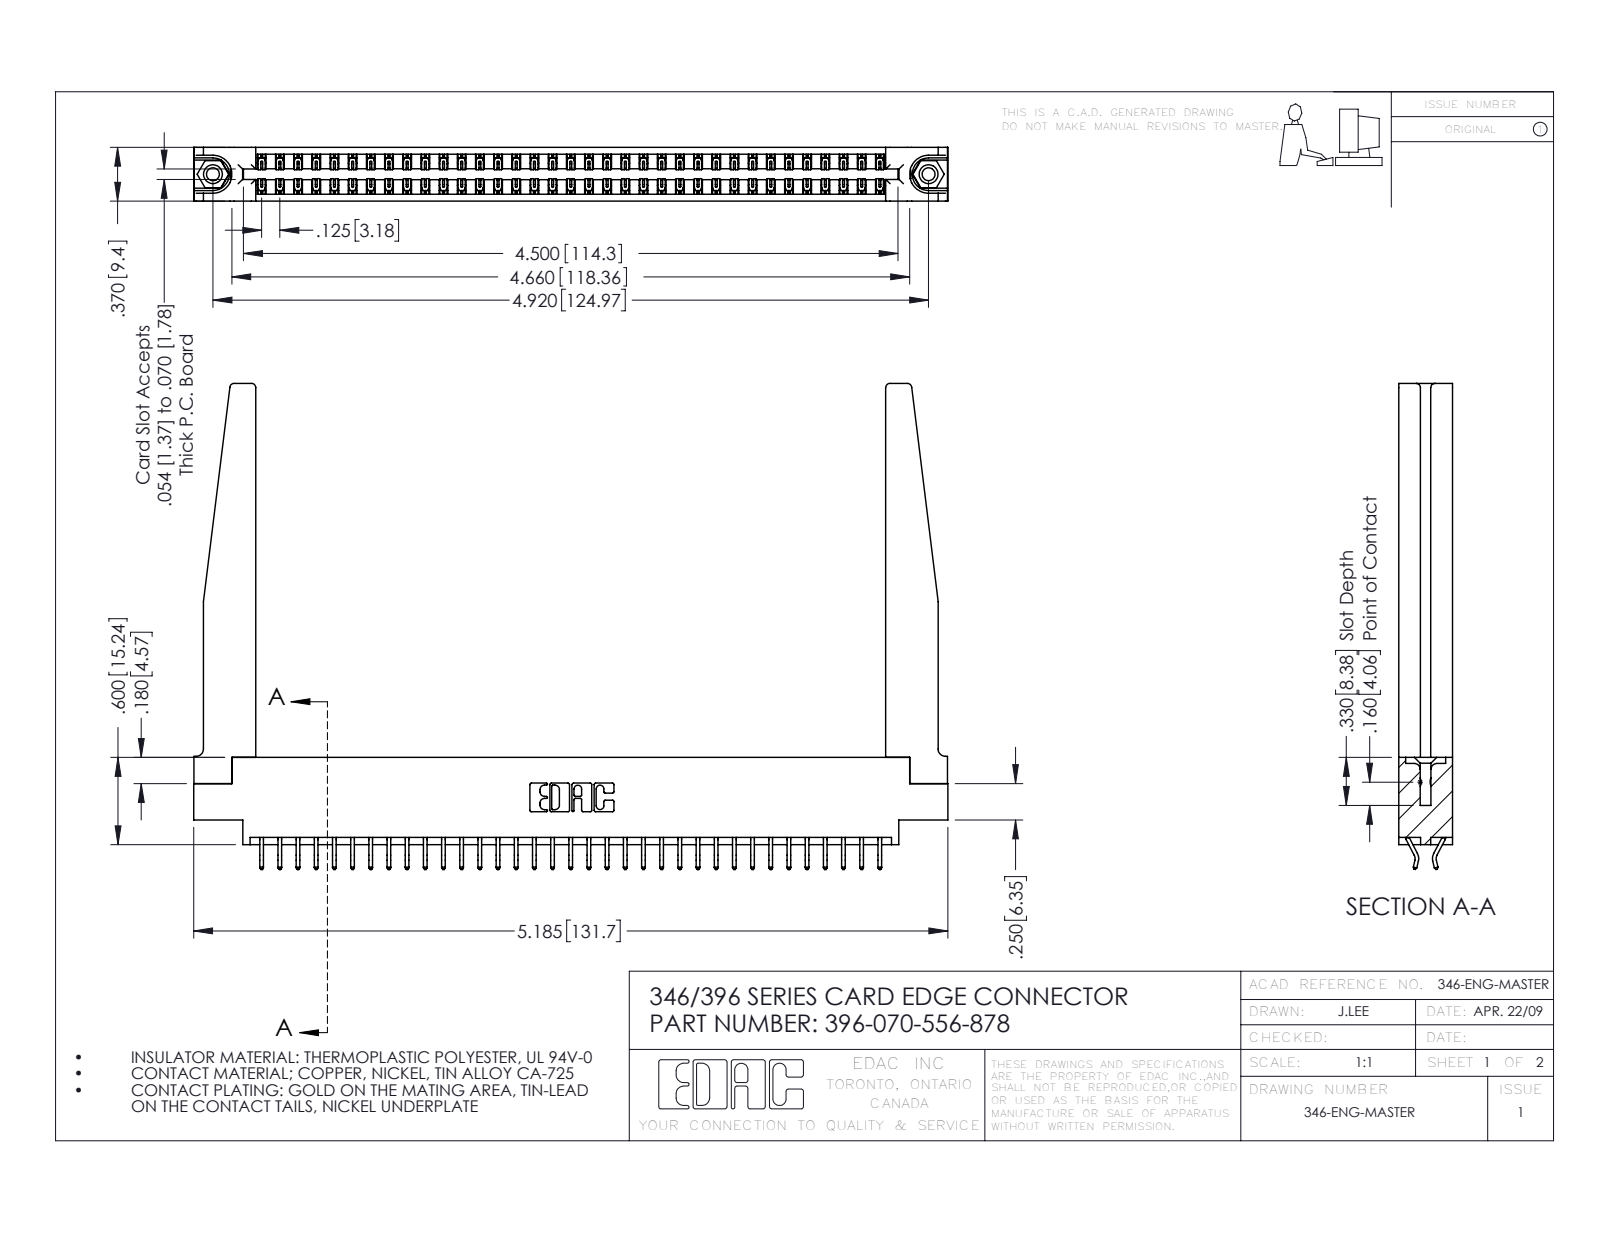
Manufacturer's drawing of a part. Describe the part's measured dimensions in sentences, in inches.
The part is named "346 Part_0.170 Offset - 0.156 Dia-TH; 345-292-001_556 Tail; 345-250-001_345-250-001-102; 396-070-556-878 (+1 more)". Its 3-D file was written by "SolidWorks 2016 (CONFIG_CONTROL_DESIGN)". It is 75 solids with 4420 faces: 2952 planar, 1416 cylindrical and 52 other. Overall it measures 5.185 by 3.34 by 0.37 inches. Its volume is 1.192 cubic inches and its surface area 37.05 square inches. Round holes: 2 of diameter 0.089, 2 of diameter 0.125, 2 of diameter 0.156, 1 of diameter 0.064. Round bosses or shafts: 2 of diameter 0.155. Partial cylindrical surfaces (rounded edges, fillets, slot ends): 105 of radius 0.006, 22 of radius 0.01, 8 of radius 0.03, 6 of radius 0.007, 6 of radius 0.031, 4 of radius 0.05, 3 of radius 0.026, 2 of radius 0.01. The main face-to-face distances are 0.37, 0.048, 0.322, 0.072, 0.148, 0.15, 0.25, 0.025, 0.298, 0.275. The hole center spacings are 0.246, 4.711, 4.92.
